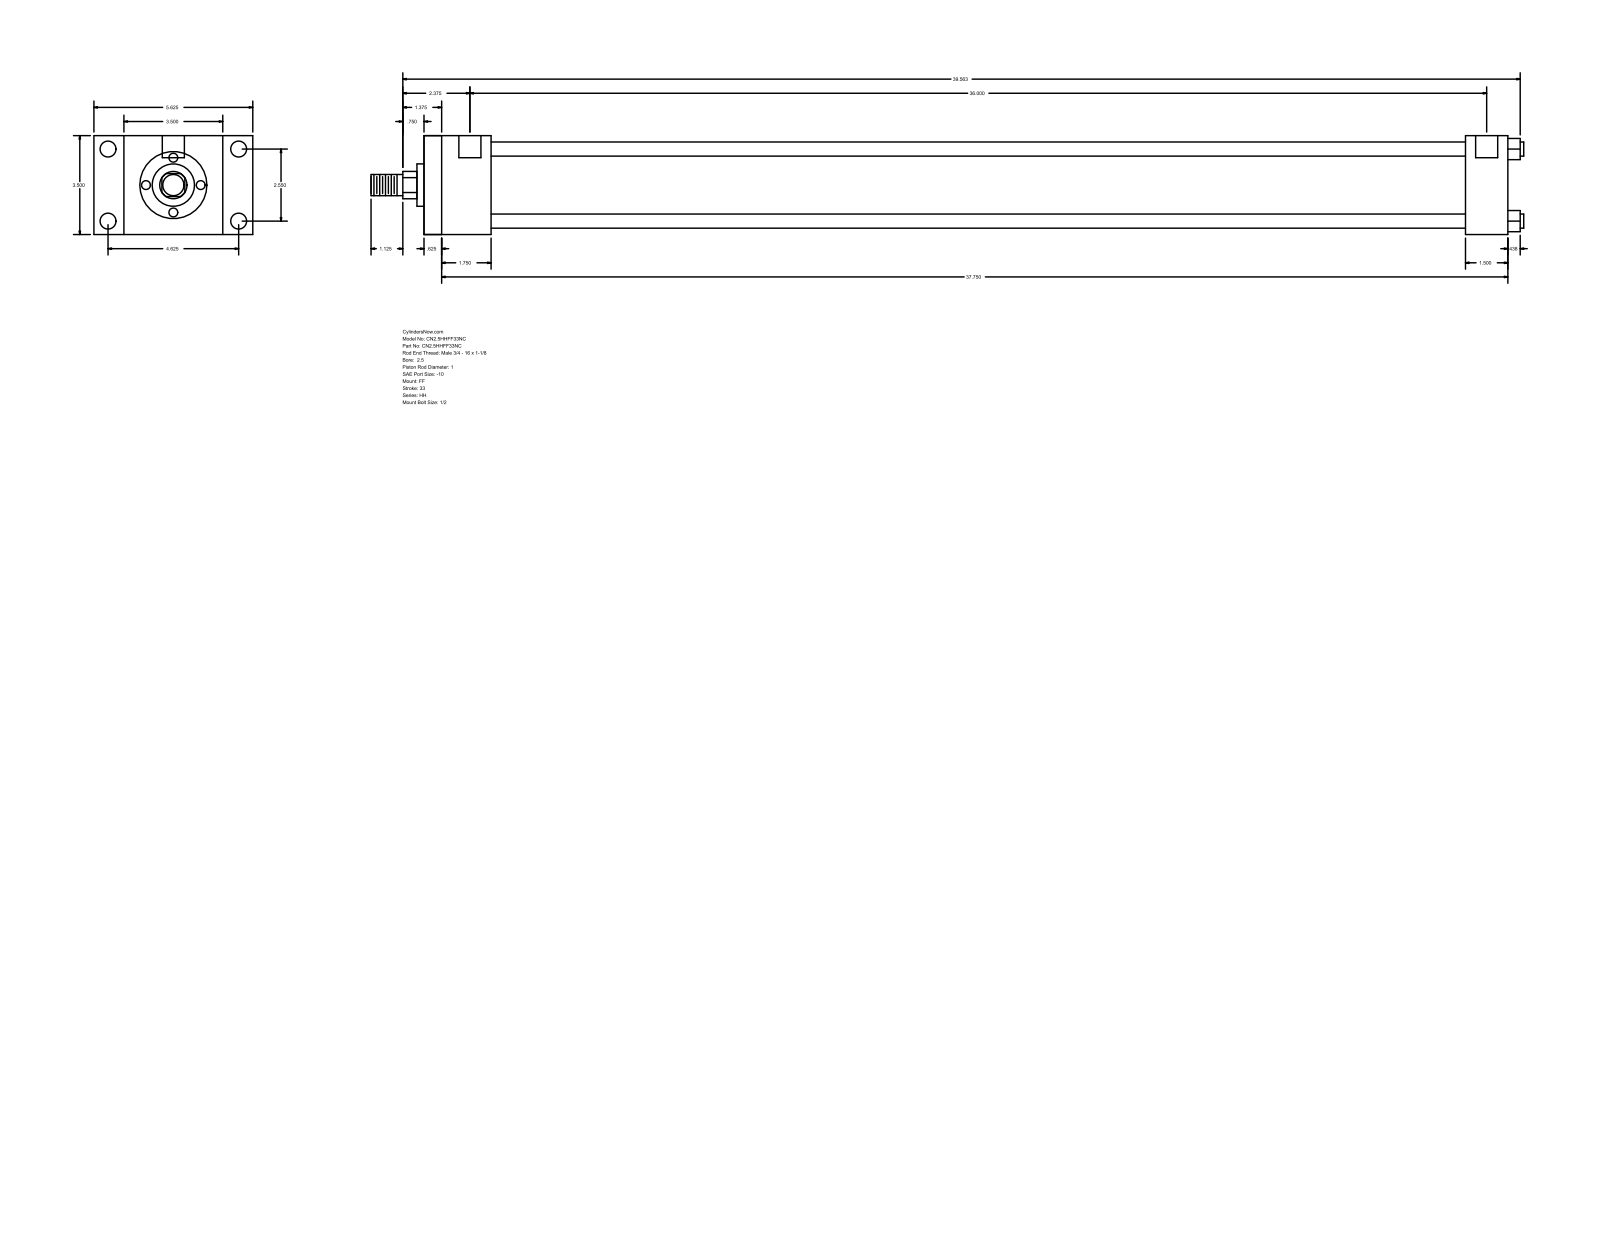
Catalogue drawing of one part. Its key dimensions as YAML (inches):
part_name: "HH_FF__0250_1"
step_written_by: "GSSL Pune (CONFIG_CONTROL_DESIGN)"
units: inches
bodies: {solids: 0, faces: 92, planar: 64, cylindrical: 28, other: 0}
overall_size: [40.813, 5.625, 3.5]
round_holes:
  - {diameter: 0.219, count: 4}
  - {diameter: 0.563, count: 4}
  - {diameter: 0.781, count: 2}
round_bosses_or_shafts:
  - {diameter: 0.5, count: 4}
  - {diameter: 2.875, count: 1}
  - {diameter: 1.5, count: 1}
  - {diameter: 1, count: 1}
  - {diameter: 0.75, count: 1}
partial_cylinders:
  - {radius: 0.484, count: 1}
face_to_face_distances: [3.5, 38.375, 0.625, 37.75, 1.5, 2.375, 1.75, 36, 36.875, 36.25]
hole_center_spacings: [2.55, 4.625, 5.281, 36.125, 0.062, 0.063, 36, 36.062]
